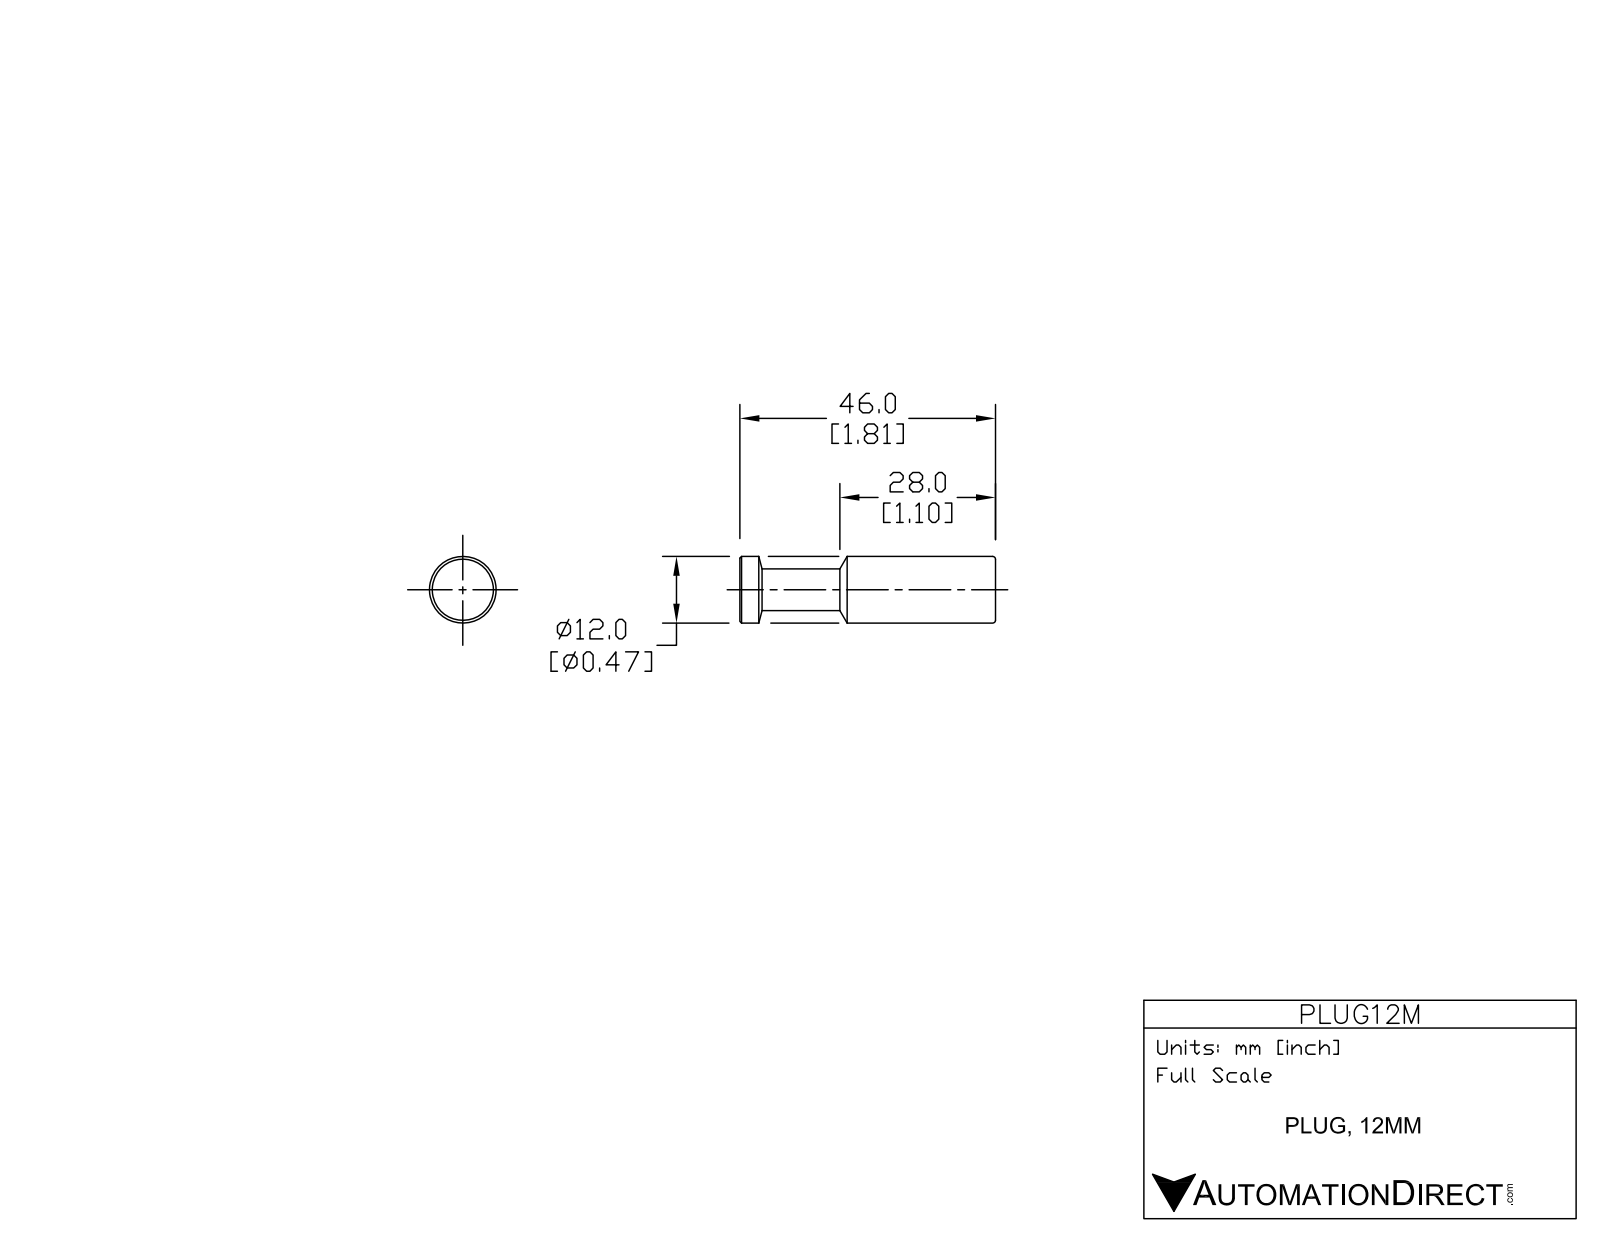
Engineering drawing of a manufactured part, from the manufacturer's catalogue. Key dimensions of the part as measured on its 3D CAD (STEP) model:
Part name (STEP PRODUCT): PLUG12M
STEP written by: SolidWorks 2015 (AUTOMOTIVE_DESIGN)
Units: inches
Bodies: 1 solid, 16 faces (2 planar, 6 cylindrical, 8 other)
Overall size (bounding box): 1.811 × 0.472 × 0.472
Volume: 0.254 in³ · Surface area: 2.831 in²
Round bosses / shafts (diameter × count): ⌀0.472 ×1, ⌀0.295 ×1
Main face-to-face distances: 1.811
